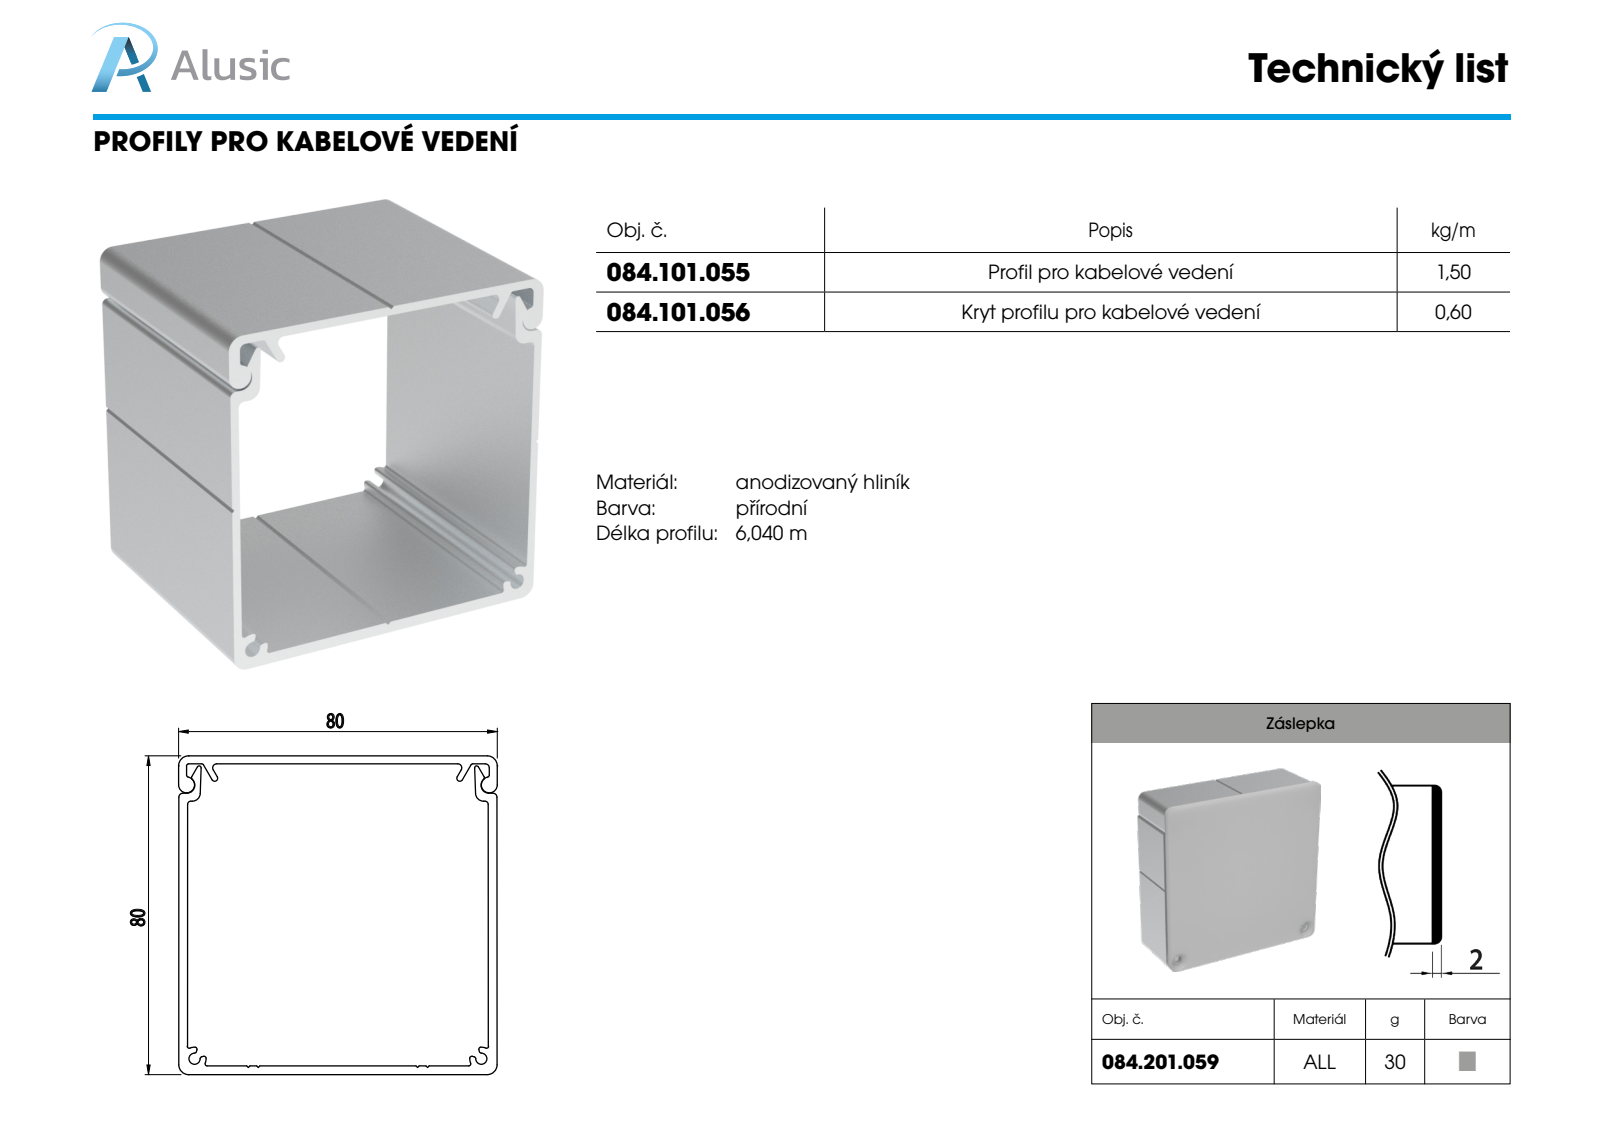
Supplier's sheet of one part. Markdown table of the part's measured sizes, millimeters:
| quantity | value |
| --- | --- |
| part name | 084.201.059 |
| STEP written by | SolidWorks 2012 (CONFIG_CONTROL_DESIGN) |
| units | millimeters |
| bodies | 1 solid, 18 faces (6 planar, 8 cylindrical, 4 other) |
| overall size | 80 × 80 × 2 |
| volume | 12 725 mm³ |
| surface area | 13 417 mm² |
| round holes (diameter × count) | 3.2 × 2 |
| partial cylindrical surfaces (radius × count) | 2.5 × 4 |
| main face-to-face distances | 2, 80 |
| hole center spacings | 72 |
